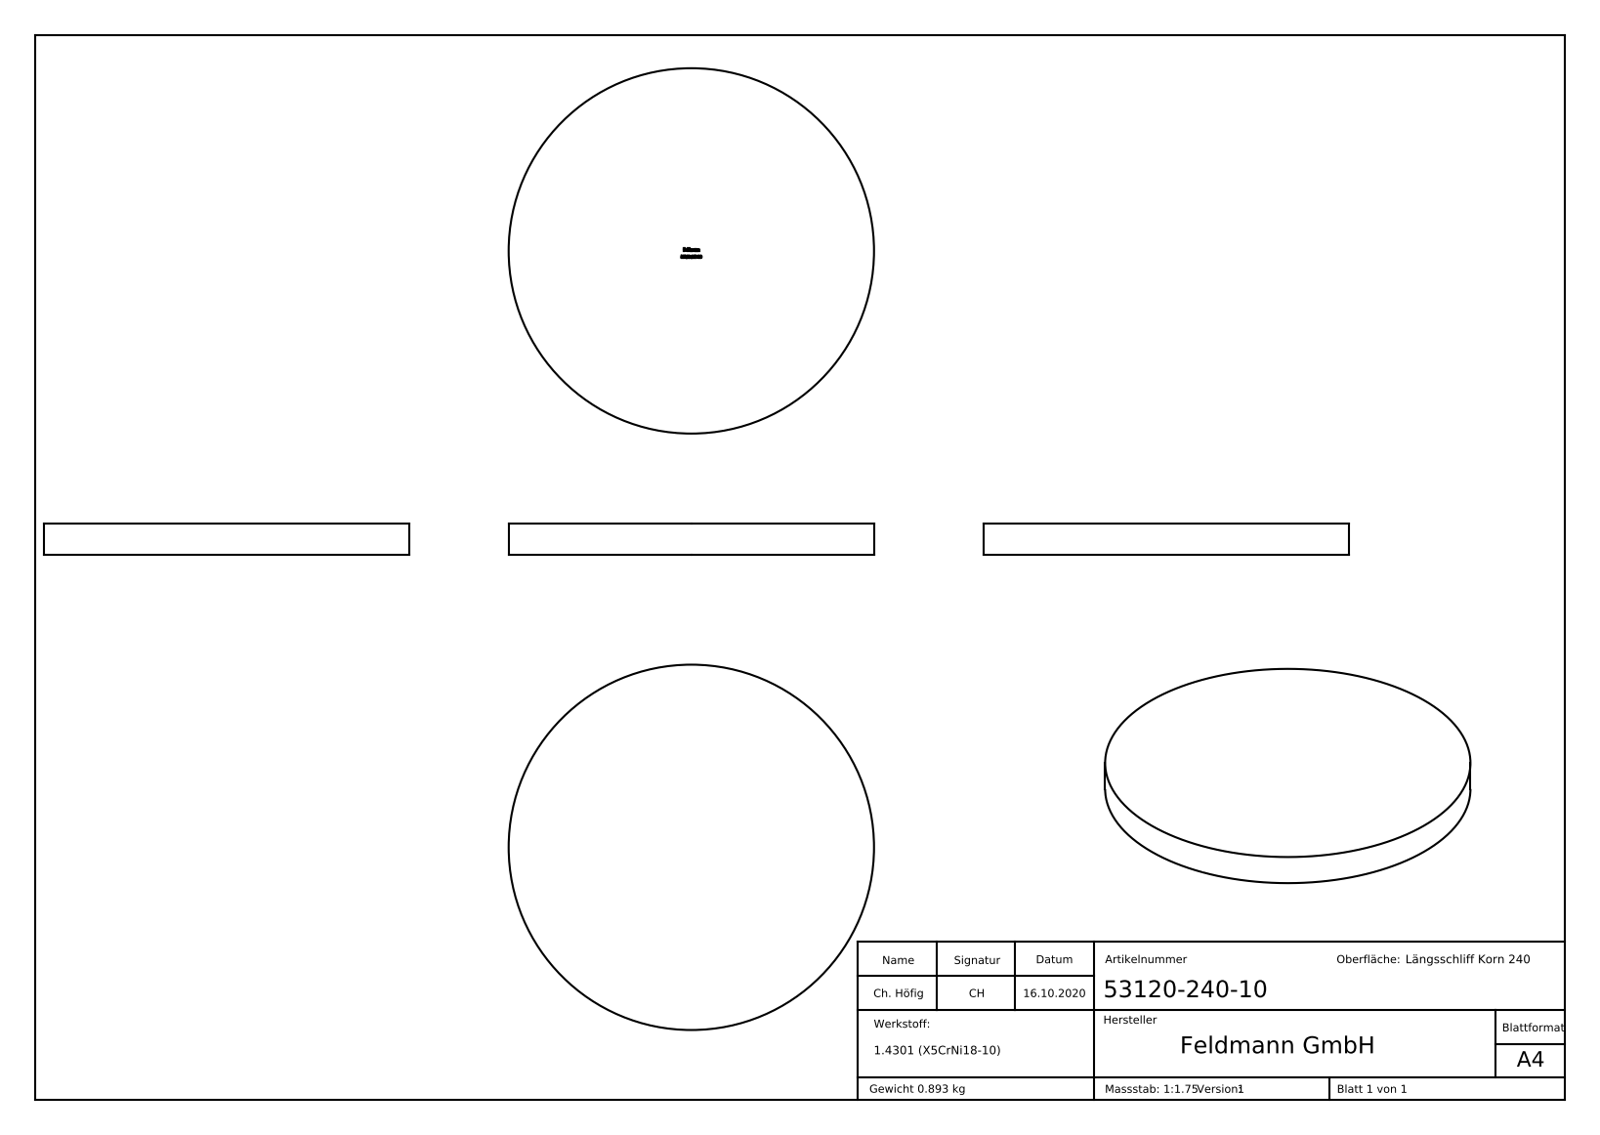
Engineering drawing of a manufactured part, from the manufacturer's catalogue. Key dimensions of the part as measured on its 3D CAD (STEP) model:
Part name (STEP PRODUCT): 53120-240-10
STEP written by: SolidWorks 2018 (CONFIG_CONTROL_DESIGN)
Units: millimetres
Bodies: 1 solid, 248 faces (137 planar, 2 cylindrical, 109 other)
Overall size (bounding box): 120 × 120 × 10
Volume: 113 097 mm³ · Surface area: 26 396 mm²
Round bosses / shafts (diameter × count): ⌀120 ×1
Main face-to-face distances: 10, 9.9, 1.06, 2.45, 0.99, 0.39, 2.77, 1.55, 1.78, 0.83
